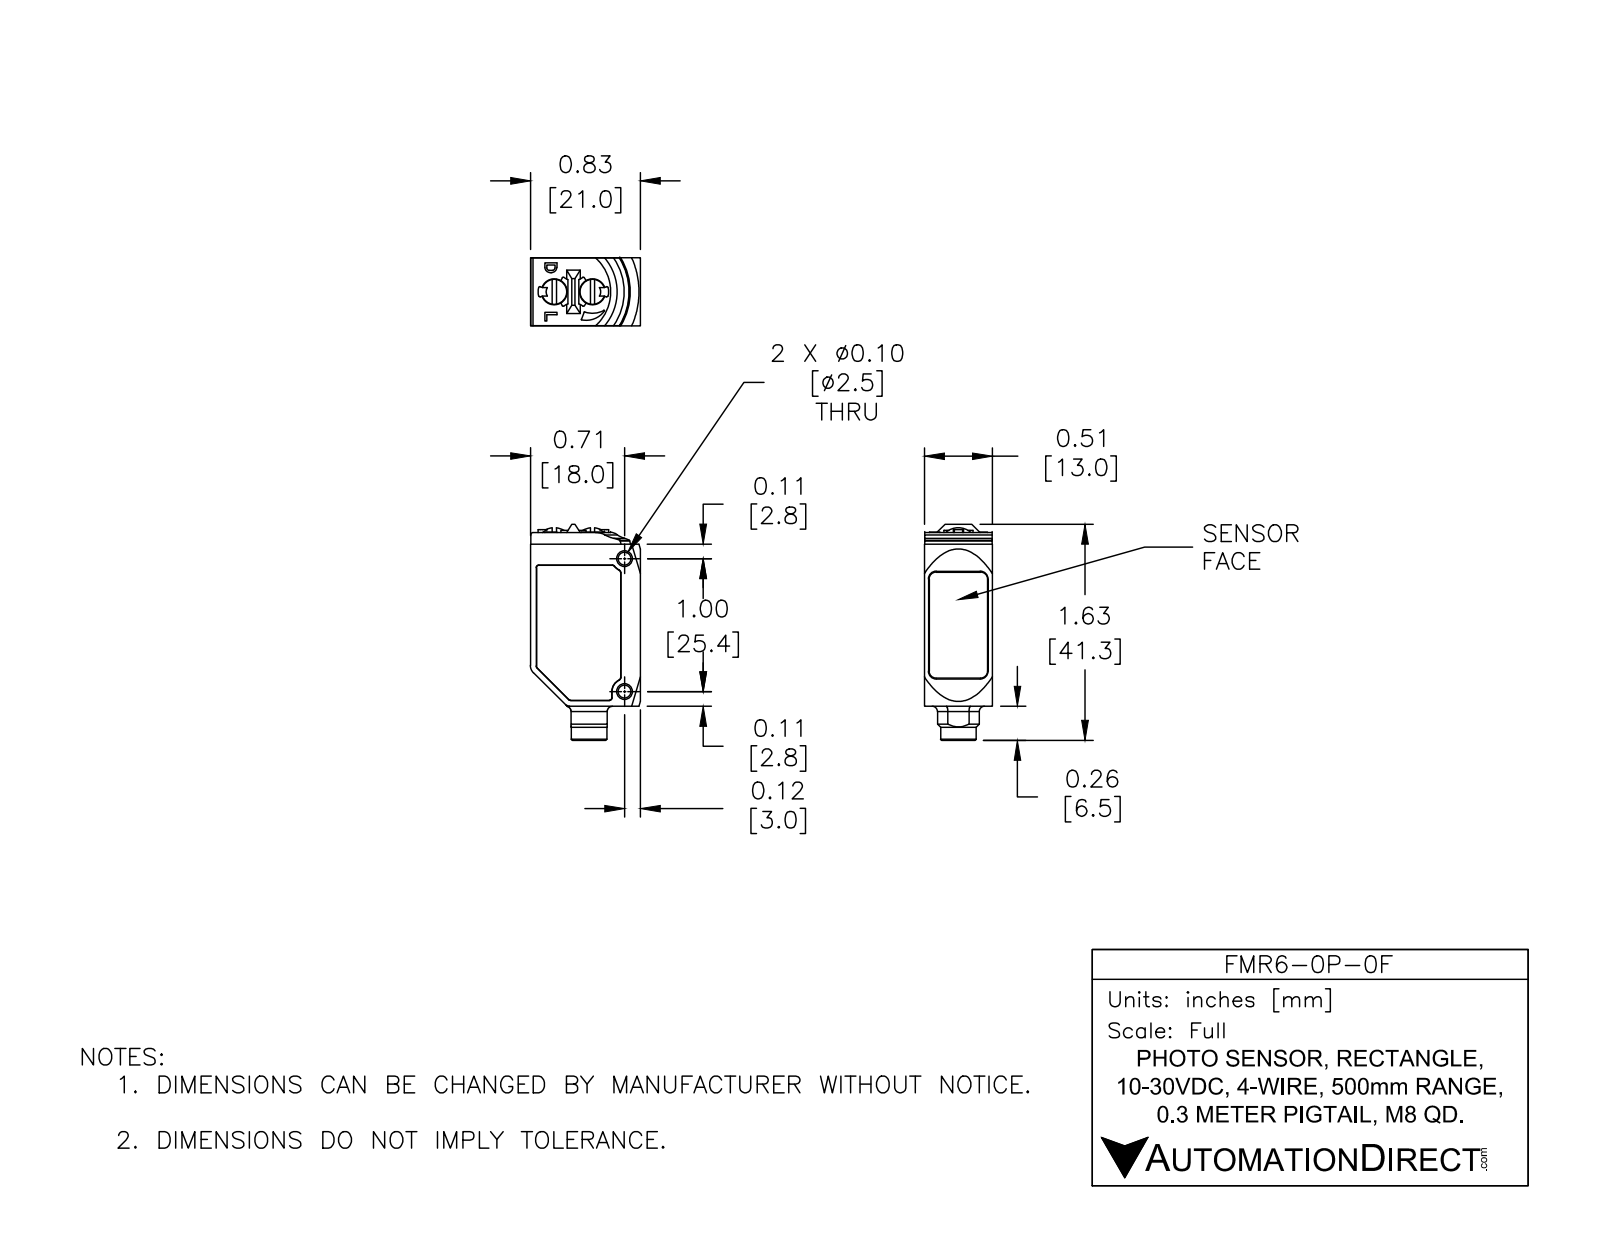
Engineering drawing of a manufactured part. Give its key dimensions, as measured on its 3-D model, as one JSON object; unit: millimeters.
{"part_name": "FMR6-0P-0F", "step_written_by": "SolidWorks 2017 (AUTOMOTIVE_DESIGN)", "units": "millimeters", "bodies": {"solids": 1, "faces": 197, "planar": 89, "cylindrical": 79, "other": 29}, "overall_size": [41.3, 21, 13], "volume_mm3": 8640, "surface_area_mm2": 3394, "round_holes": [[2.5, 2], [5, 2], [5.8, 1]], "round_bosses_or_shafts": [[4.8, 2], [6.8, 1]], "partial_cylinders_radius": [[0.5, 7], [0.5, 7], [1, 5], [0.2, 4], [0.3, 4], [1.3, 4], [1.5, 4], [0.1, 3]], "face_to_face_distances": [13, 21, 33.2, 13, 0.8, 12.2, 0.9, 0.9, 12, 0.8], "hole_center_spacings": [0.7, 6.7, 7.3, 25.4]}
